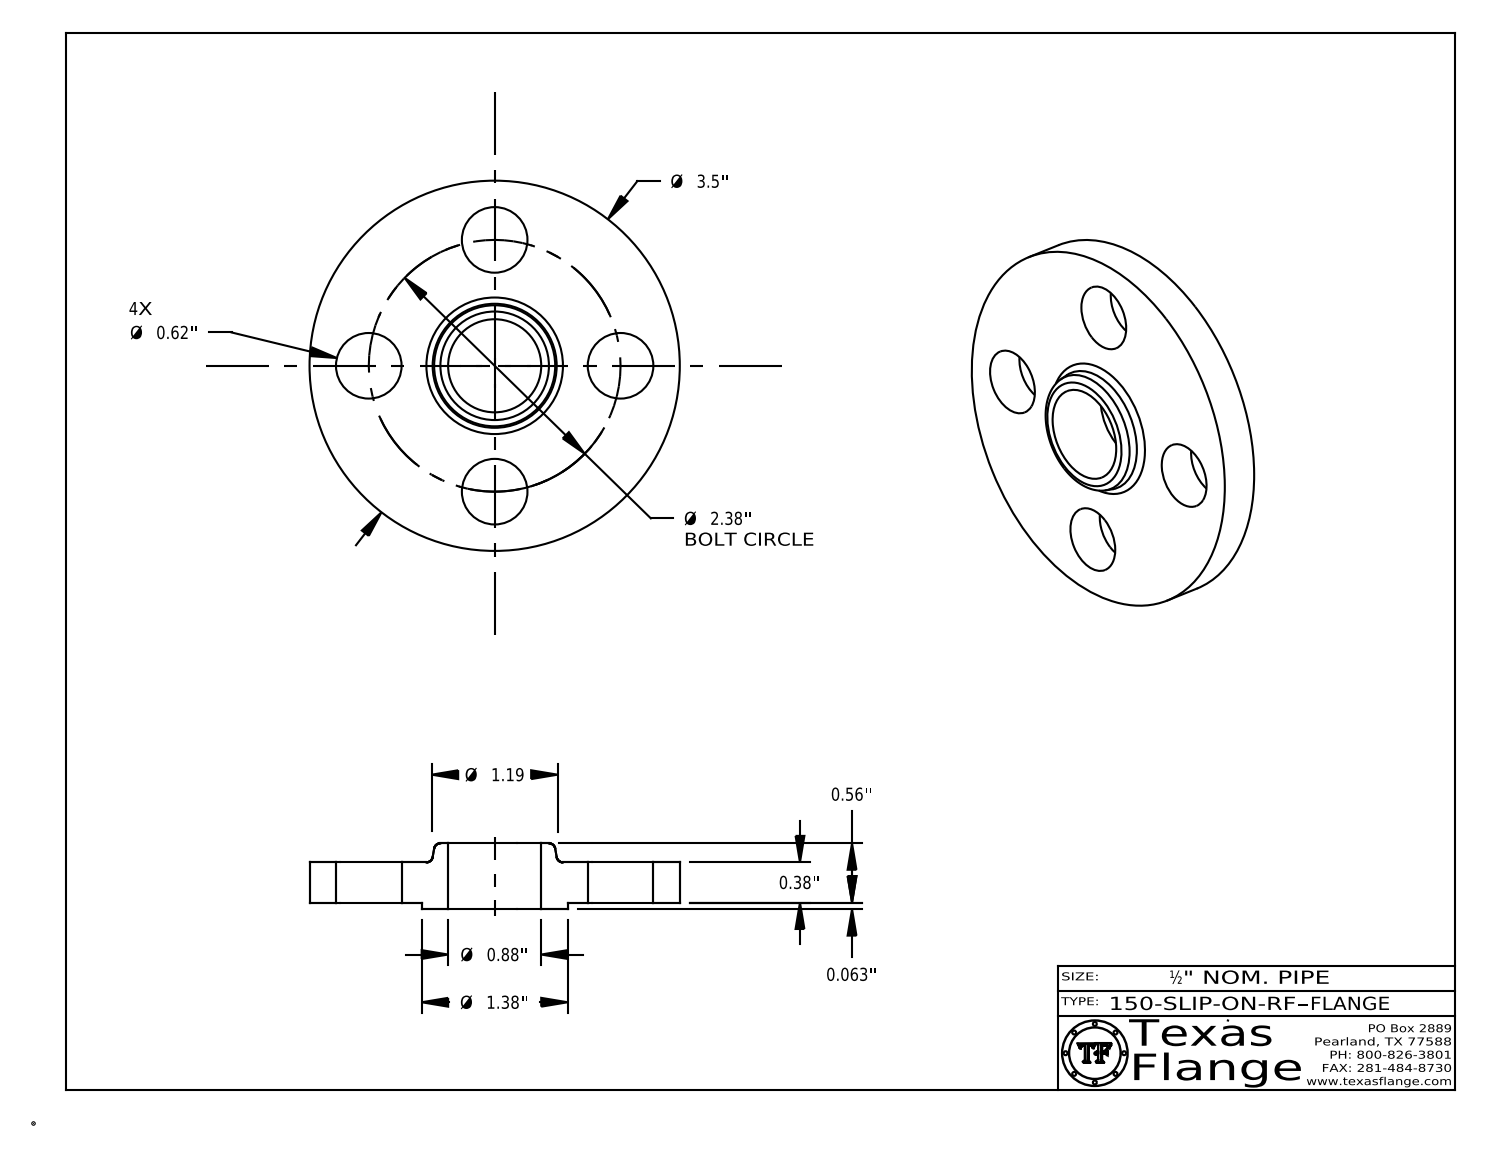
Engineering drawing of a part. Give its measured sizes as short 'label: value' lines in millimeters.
name: 150-SLIP-ON-RF
written by: CATIA V5 STEP AP214 (AUTOMOTIVE_DESIGN)
unit: mm
bodies: 1 solid, 409 faces (369 planar, 34 cylindrical, 6 other)
size: 88.9 × 88.9 × 15.8
volume: 50 820 mm³; area: 16 300 mm²
holes: 4× ⌀15.7, 1× ⌀12.6, 1× ⌀22.4
bosses: 8× ⌀0.8, 1× ⌀88.9, 1× ⌀35.1, 1× ⌀9.9
face distances: 9.7, 1.6, 11.3, 15.8, 14.2, 4.6, 10.9, 9.3, 0.4, 5
hole spacings: 30.2, 42.7, 23.1, 55.9, 60.5, 30.2
